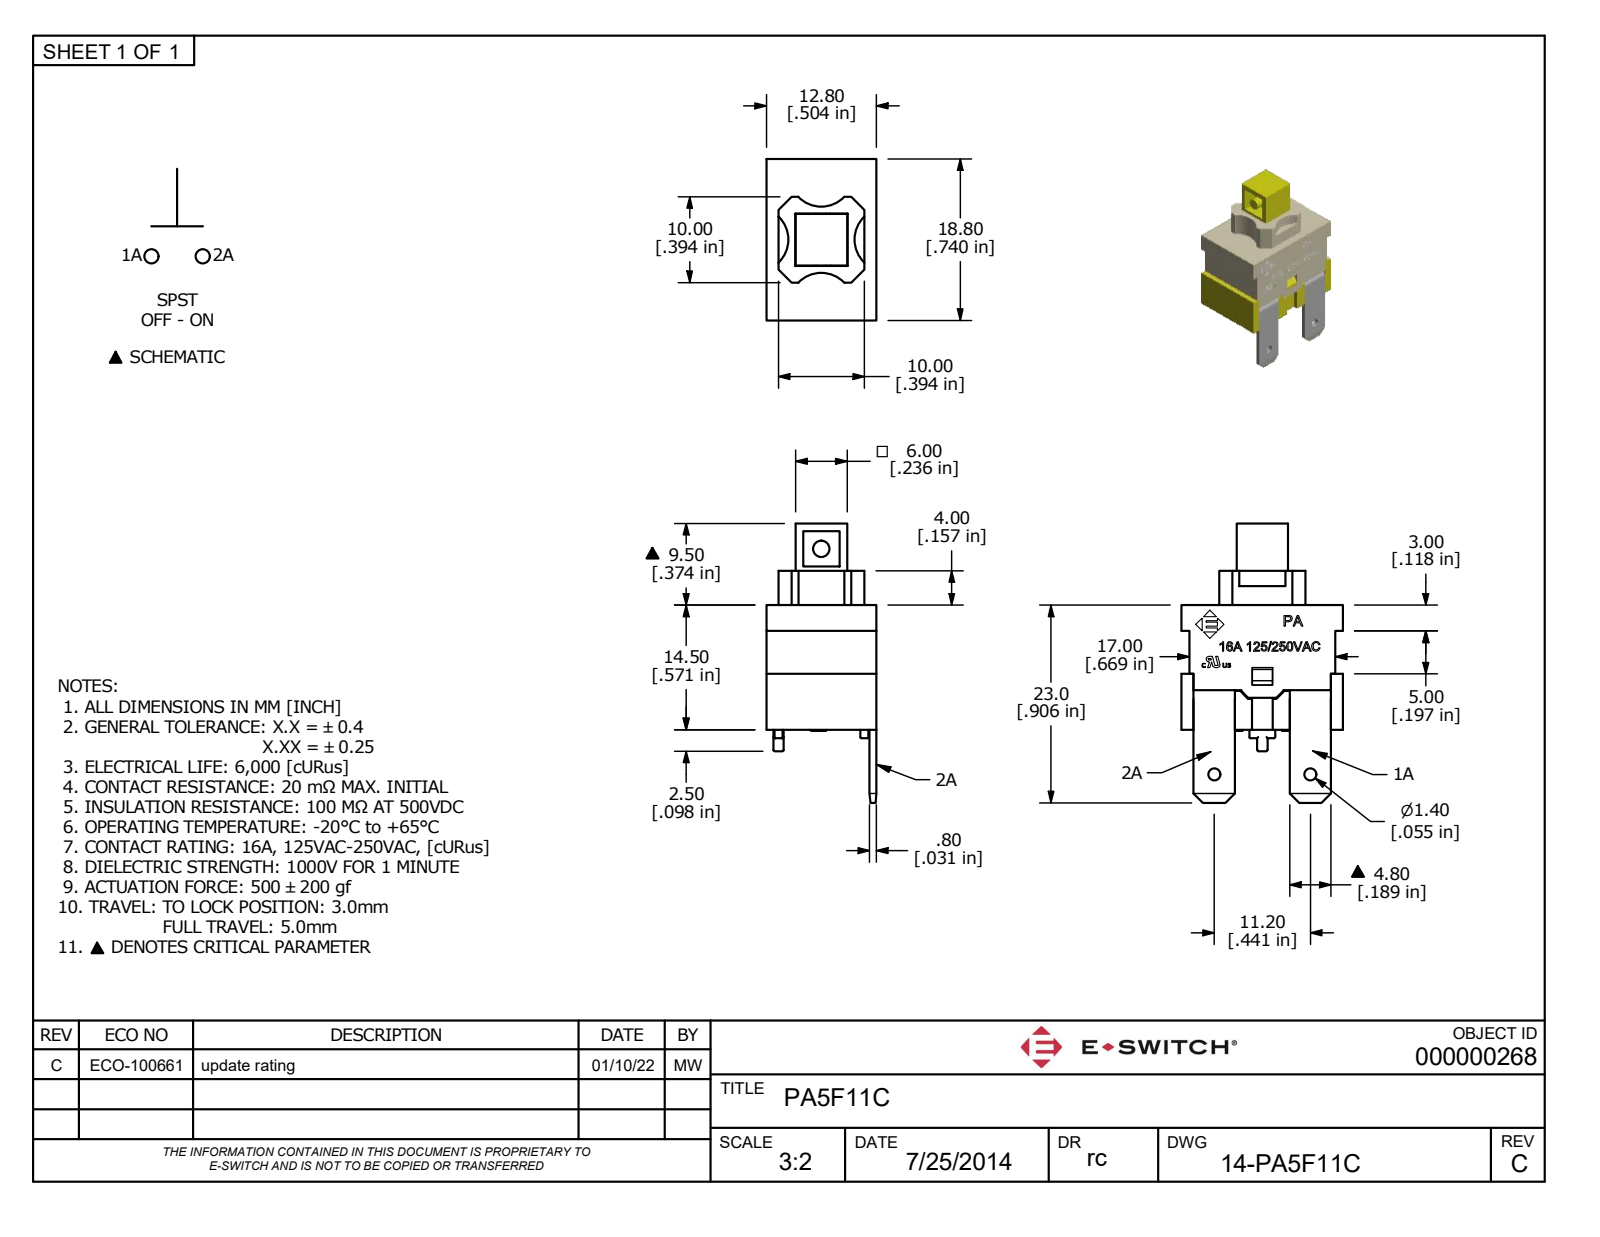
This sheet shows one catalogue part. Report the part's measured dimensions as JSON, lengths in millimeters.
{"part_name": "PA5F11C", "step_written_by": "Autodesk Inventor 2022 (AUTOMOTIVE_DESIGN)", "units": "millimeters", "bodies": {"solids": 1, "faces": 745, "planar": 546, "cylindrical": 69, "other": 130}, "overall_size": [32.5, 18.8, 12.8], "volume_mm3": 2096, "surface_area_mm2": 4273, "round_holes": [[1.4, 2], [3, 1]], "round_bosses_or_shafts": [[0.95, 4], [2.5, 1], [1.9, 1]], "partial_cylinders_radius": [[0.25, 20], [0.12, 16], [0.15, 8], [3.71, 4], [1, 2], [0.5, 1], [1.79, 1], [2.32, 1]], "face_to_face_distances": [0.8, 12, 0.9, 16.8, 2, 5.5, 8.6, 11.05, 1.1, 12.8], "hole_center_spacings": [11.2]}
